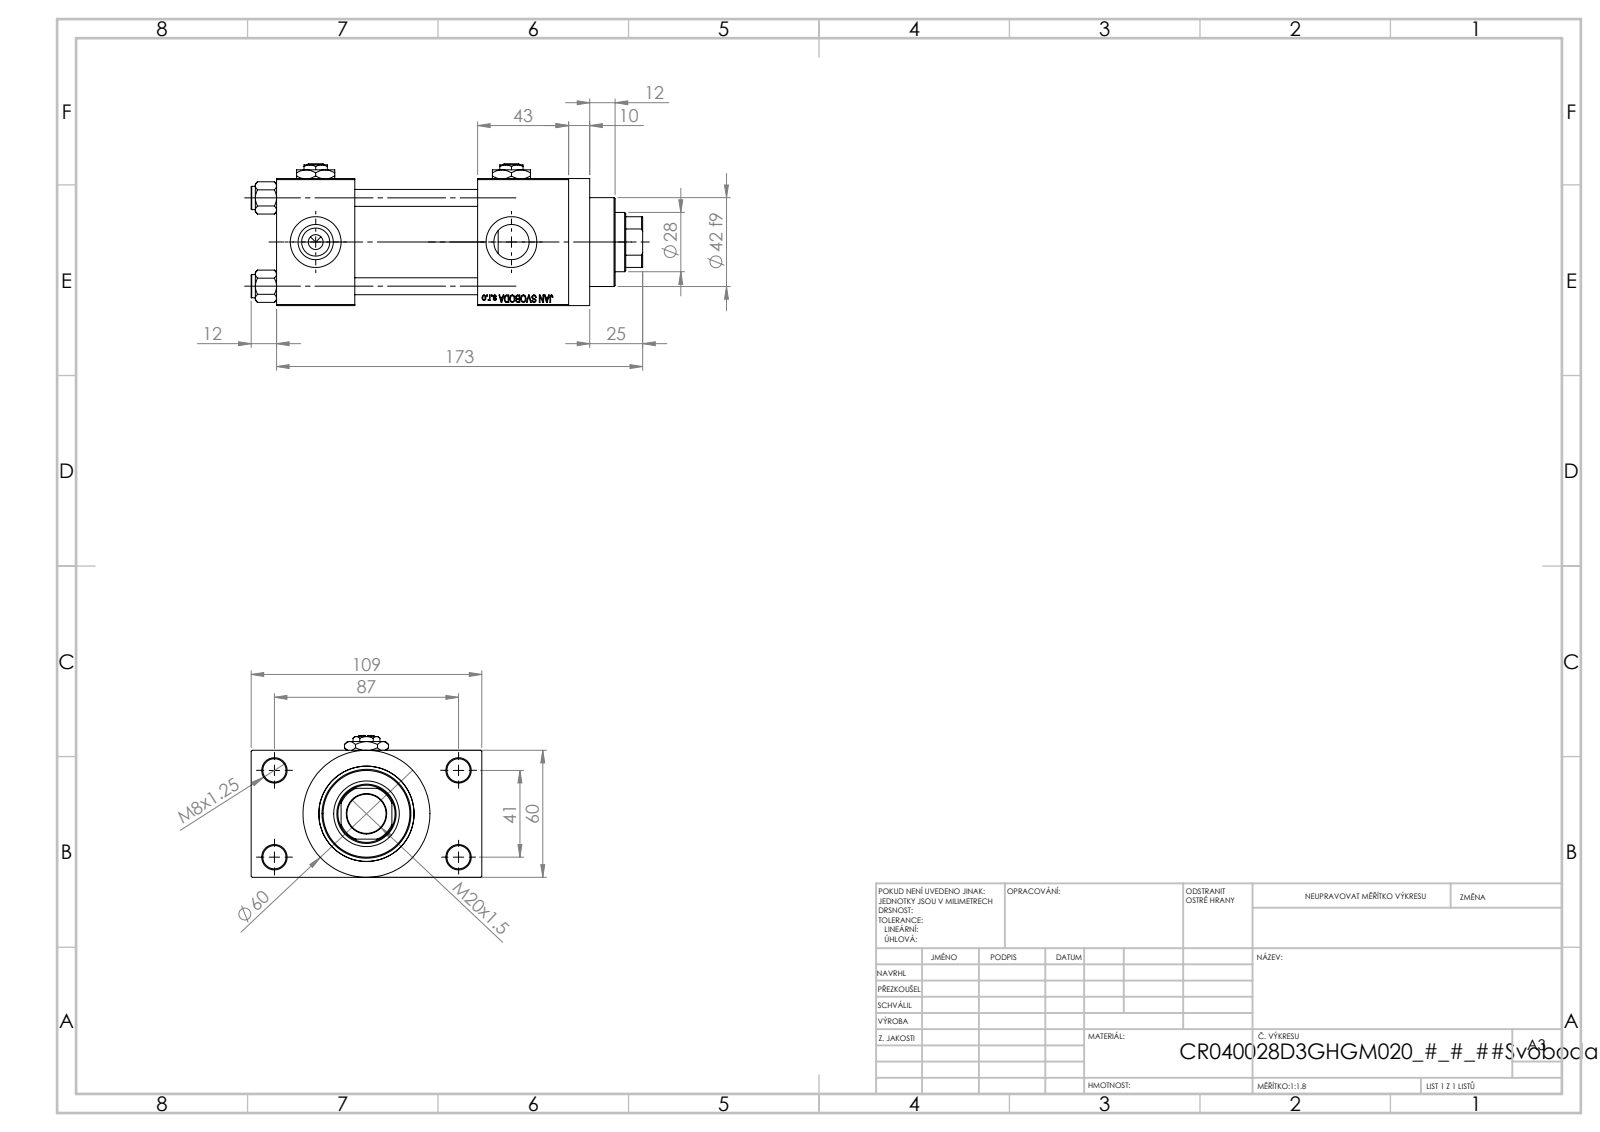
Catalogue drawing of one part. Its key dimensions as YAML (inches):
part_name: "Zatka_pro_OIL_PORT; V215CR_VCP_D; V215CR_D_TYCINKA; V215CR_D_Body (+2 more)"
step_written_by: "SolidWorks 2019 (CONFIG_CONTROL_DESIGN)"
units: inches
bodies: {solids: 13, faces: 1205, planar: 546, cylindrical: 99, other: 560}
overall_size: [7.283, 4.291, 2.638]
volume: 32.14
surface_area: 204.2
round_holes:
  - {diameter: 0.315, count: 4}
  - {diameter: 0.433, count: 4}
  - {diameter: 0.656, count: 4}
  - {diameter: 0.945, count: 4}
  - {diameter: 0.276, count: 3}
  - {diameter: 0.728, count: 1}
  - {diameter: 1.102, count: 1}
  - {diameter: 1.22, count: 1}
  - {diameter: 1.575, count: 1}
  - {diameter: 1.772, count: 1}
round_bosses_or_shafts:
  - {diameter: 0.433, count: 4}
  - {diameter: 2.362, count: 1}
  - {diameter: 1.811, count: 1}
  - {diameter: 1.654, count: 1}
partial_cylinders:
  - {radius: 0.531, count: 1}
face_to_face_distances: [2.362, 2.283, 0.965, 3.327, 1.457, 3.74, 5.433, 3.976, 1.693, 4.291]
hole_center_spacings: [0.892, 1.161, 1.642, 1.856, 1.893, 2.533, 3.011, 1.614]
